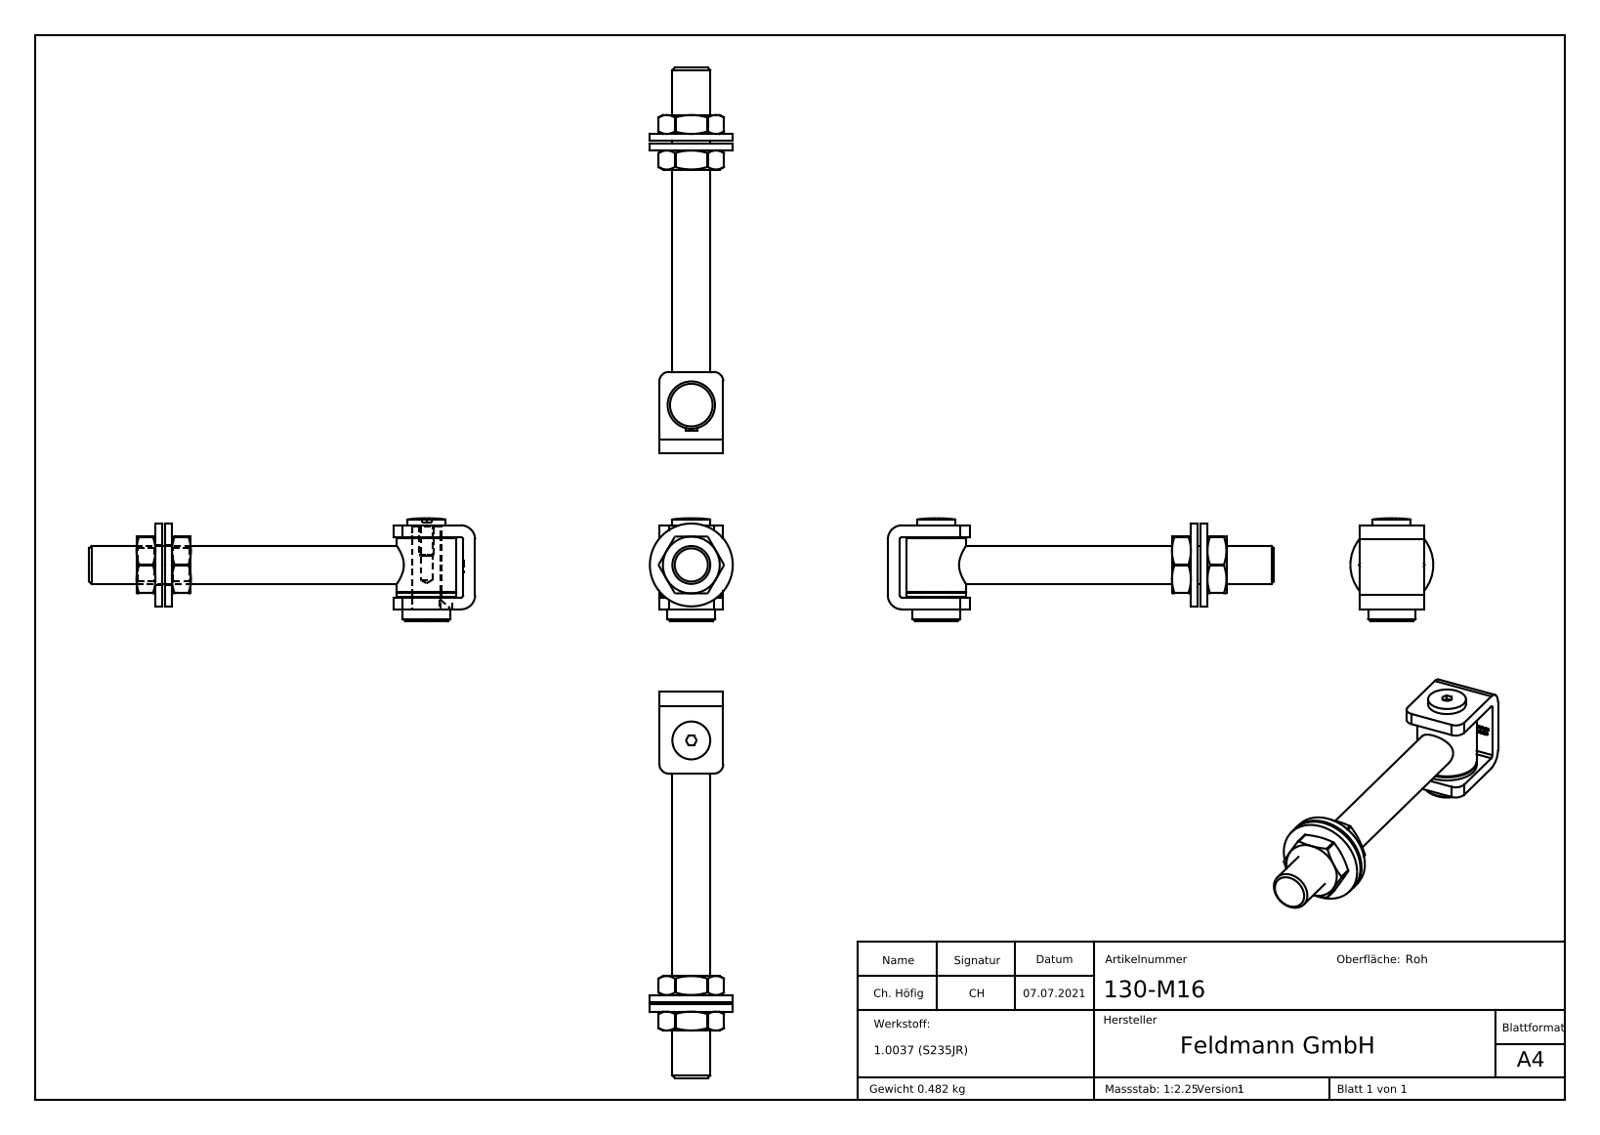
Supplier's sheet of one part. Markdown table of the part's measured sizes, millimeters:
| quantity | value |
| --- | --- |
| part name | 130-Mxx Teil6_130-M16-FEV Teil6; Torband Teil2_130-M16-FEV Teil2; Torband Teil5_130-M16-FEV Teil5; 130-M16-FEV (+4 more) |
| STEP written by | SolidWorks 2018 (CONFIG_CONTROL_DESIGN) |
| units | millimeters |
| bodies | 9 solids, 550 faces (348 planar, 39 cylindrical, 163 other) |
| overall size | 163 × 42.46 × 35 |
| volume | 60 558 mm³ |
| surface area | 27 575 mm² |
| round holes (diameter × count) | 5 × 1, 8 × 1, 12.5 × 1, 14 × 1, 17 × 1 |
| round bosses / shafts (diameter × count) | 35 × 1, 25 × 1, 20.5 × 1, 20 × 1, 16 × 1, 11.8 × 1, 6 × 1 |
| partial cylindrical surfaces (radius × count) | 0.5 × 6, 1 × 2, 4 × 2, 6 × 2 |
| main face-to-face distances | 5, 2.5, 3.5, 30.5, 6, 35.5, 8, 5.67, 29.83, 0.67 |
| hole center spacings | 1.33 |
